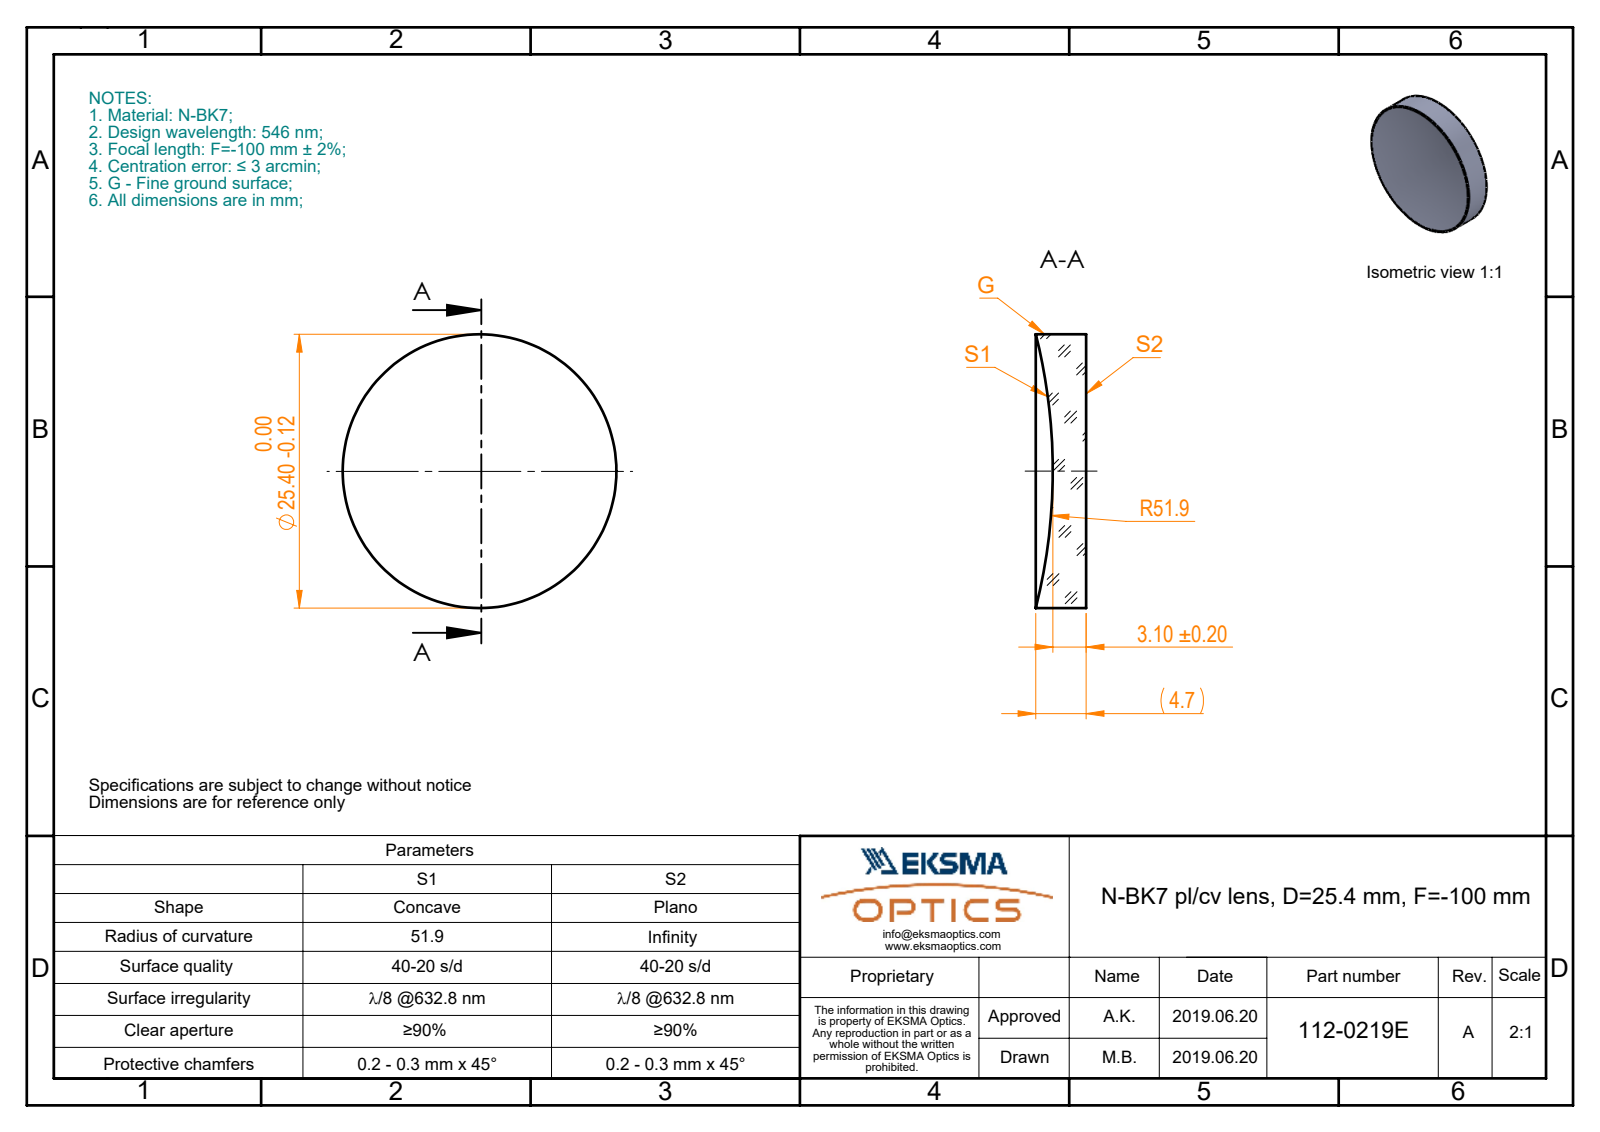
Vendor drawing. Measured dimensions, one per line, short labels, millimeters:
name: 112-0219E BK7 pl-cv 25.4 F-100
written by: SolidWorks 2017 (CONFIG_CONTROL_DESIGN)
unit: mm
bodies: 1 solid, 5 faces (1 planar, 2 cylindrical, 2 other)
size: 12.7 × 12.7 × 3.41
volume: 412 mm³; area: 390 mm²
bosses: 1× ⌀12.7
